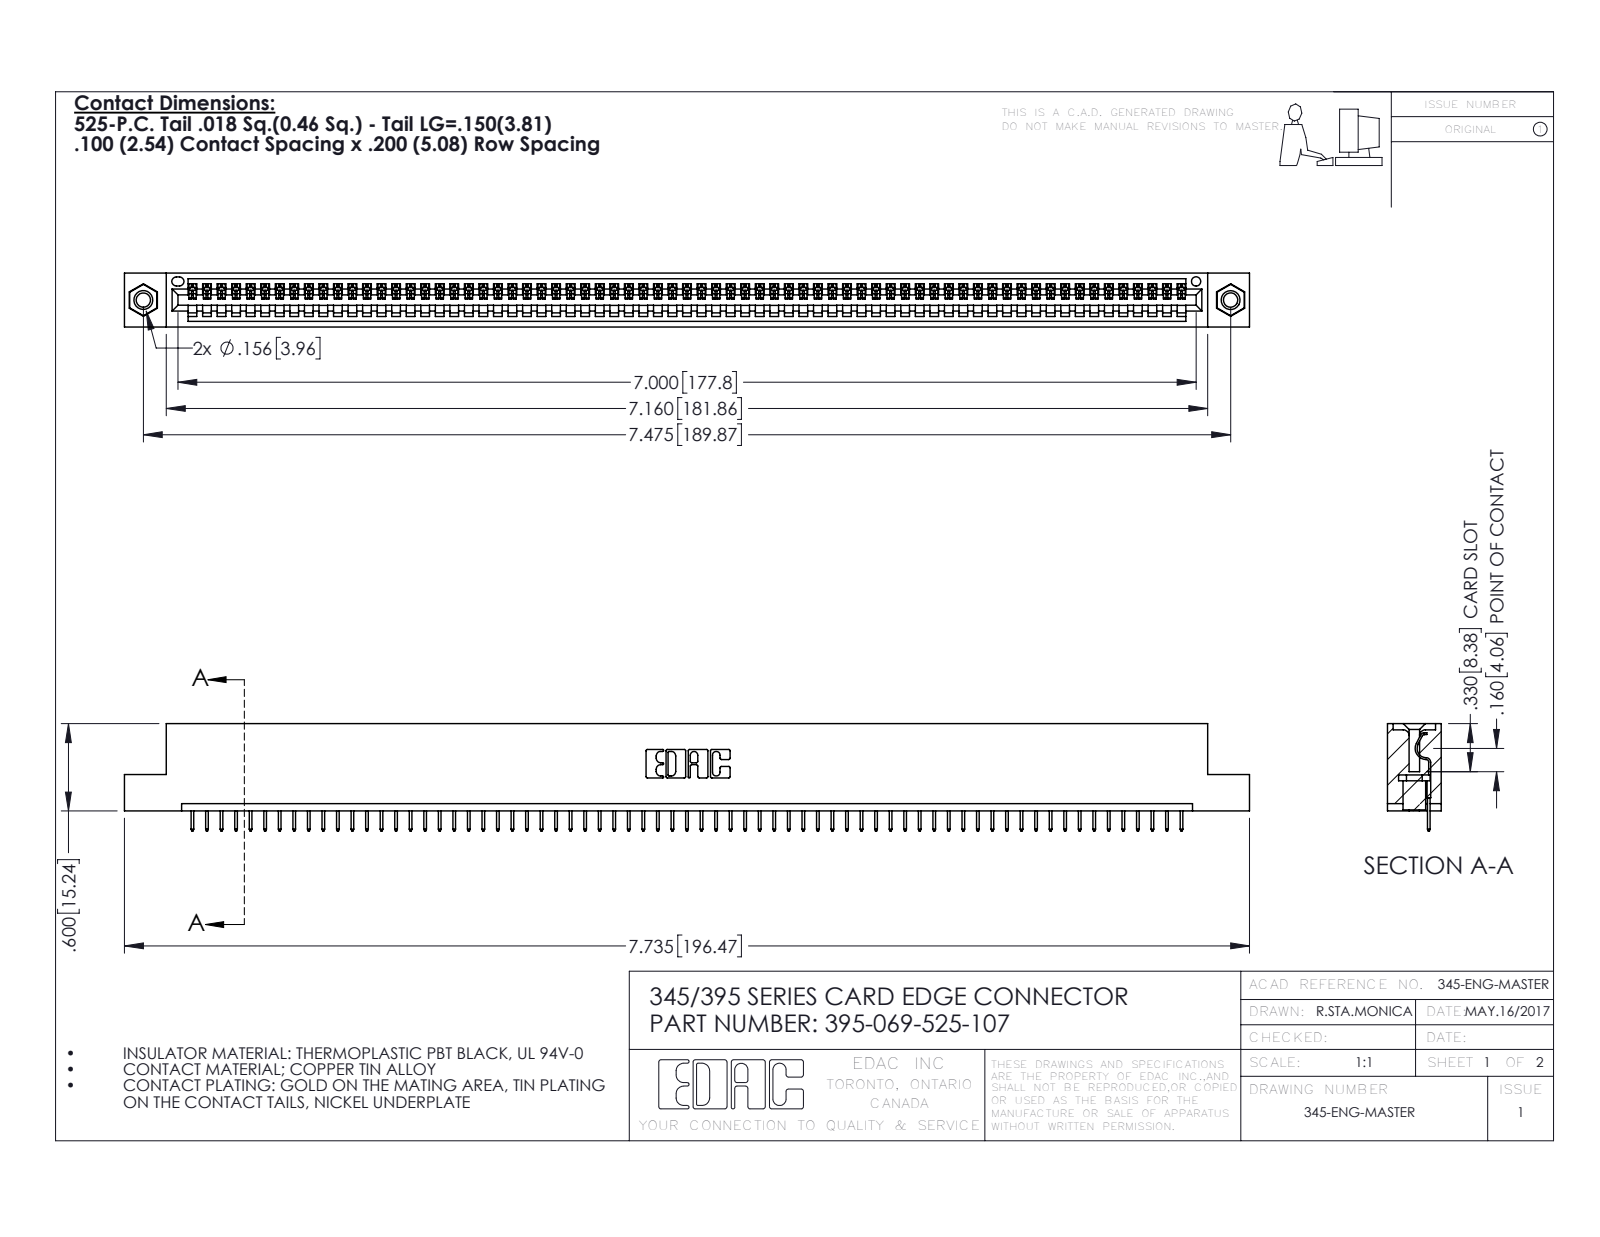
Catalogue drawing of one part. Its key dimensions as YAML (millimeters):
part_name: "345-292-001_345-293-125; 345 Part_Flush Mounting Lugs - 0.156 Dia-TI; 395-069-525-107; 345-250-001_345-250-005-103"
step_written_by: "SolidWorks 2020 (CONFIG_CONTROL_DESIGN)"
units: millimeters
bodies: {solids: 72, faces: 4464, planar: 3286, cylindrical: 1162, other: 16}
overall_size: [196.5, 18.7, 9.4]
volume: 18580
surface_area: 24160
round_holes:
  - {diameter: 2.5, count: 2}
  - {diameter: 3.2, count: 2}
  - {diameter: 4, count: 2}
  - {diameter: 1.6, count: 1}
round_bosses_or_shafts:
  - {diameter: 3.9, count: 2}
partial_cylinders:
  - {radius: 0.2, count: 138}
  - {radius: 0.3, count: 22}
  - {radius: 0.2, count: 6}
  - {radius: 0.8, count: 6}
  - {radius: 0.7, count: 3}
  - {radius: 0.8, count: 2}
  - {radius: 1, count: 2}
  - {radius: 0.4, count: 1}
face_to_face_distances: [1.8, 7.6, 9.4, 5.1, 2.5, 6.9, 0.6, 5.7, 1.8, 3.8]
hole_center_spacings: [6.9, 183.9, 189.9]
